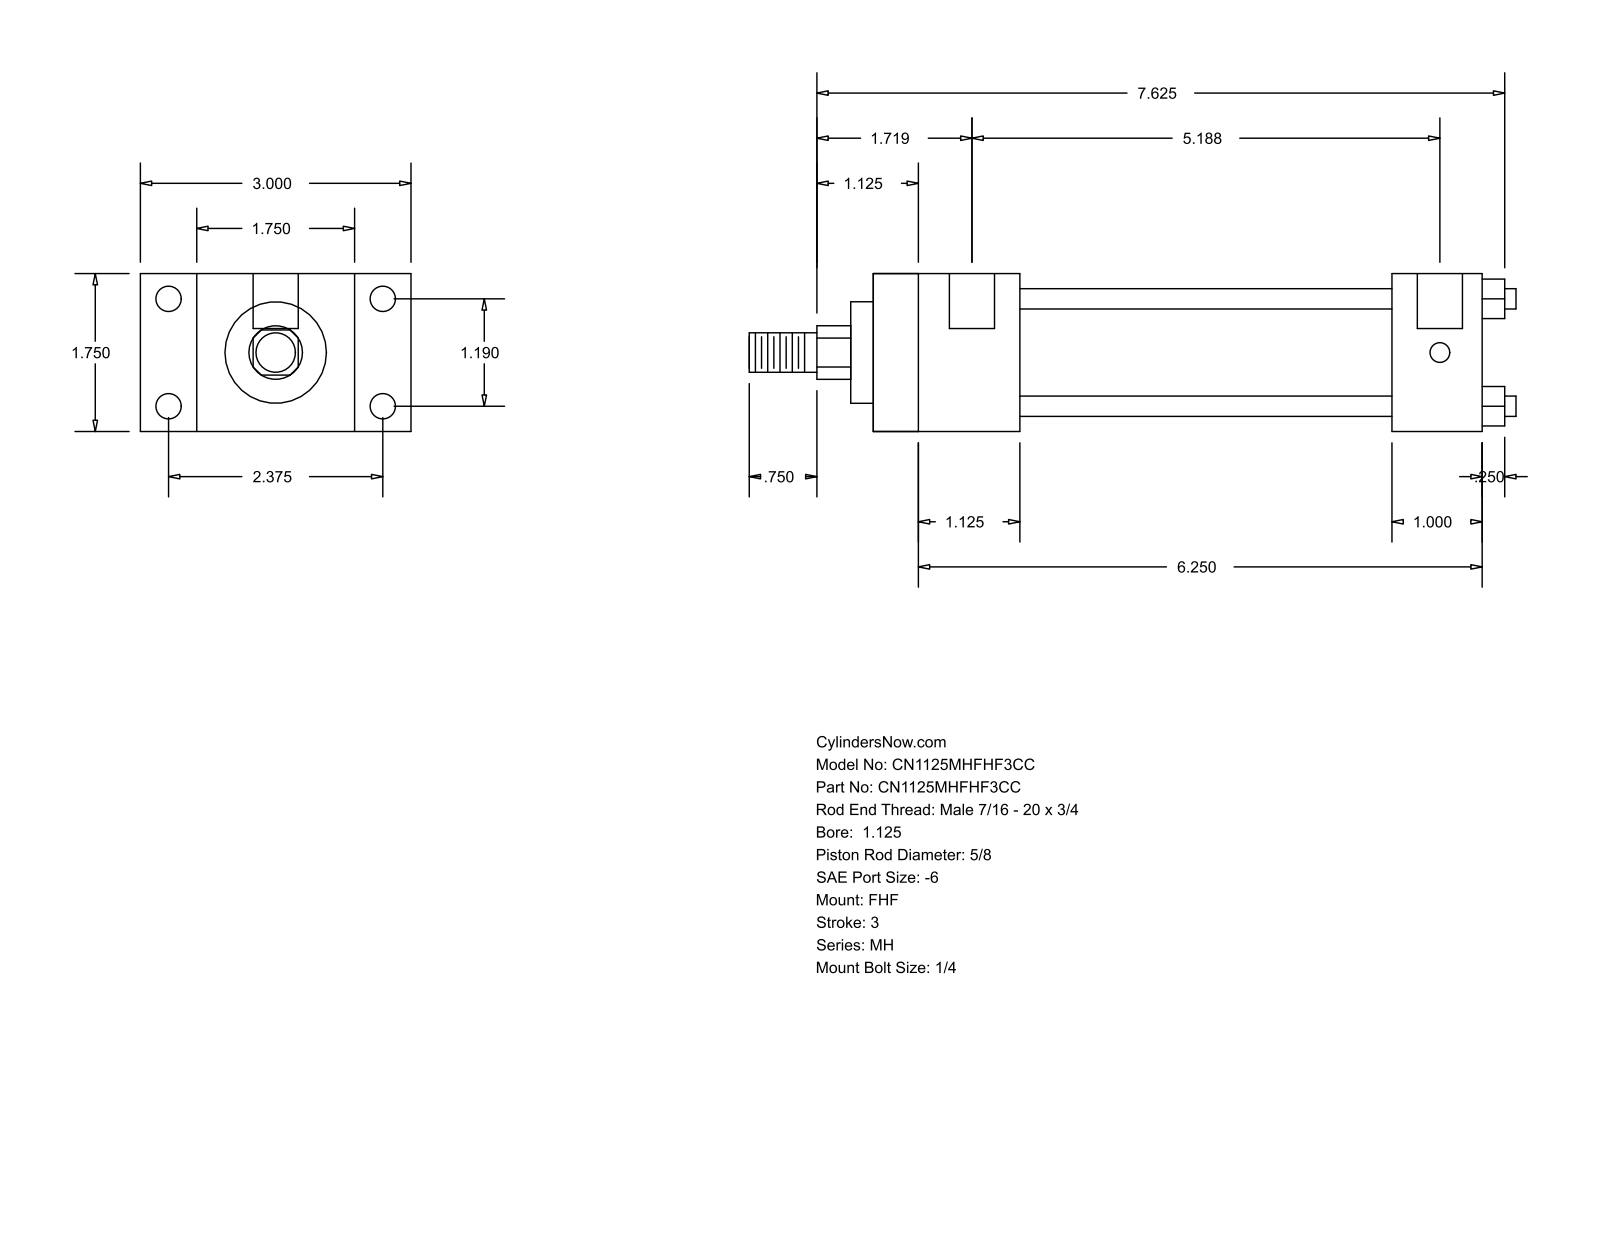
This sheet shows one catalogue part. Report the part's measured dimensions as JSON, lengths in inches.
{"part_name": "MH_FHF__0112_0.625", "step_written_by": "GSSL Pune (CONFIG_CONTROL_DESIGN)", "units": "inches", "bodies": {"solids": 0, "faces": 88, "planar": 60, "cylindrical": 28, "other": 0}, "overall_size": [8.5, 3, 1.75], "round_holes": [[0.219, 4], [0.281, 4], [0.5, 2]], "round_bosses_or_shafts": [[0.225, 4], [1.375, 1], [1.125, 1], [0.625, 1], [0.437, 1]], "partial_cylinders_radius": [[0.297, 1]], "face_to_face_distances": [1.75, 0.625, 2.375, 1.625, 3, 6.75, 5.125, 5.75, 4.125, 1], "hole_center_spacings": [1.19, 2.375, 2.656, 5.063, 0.125, 5.187]}
